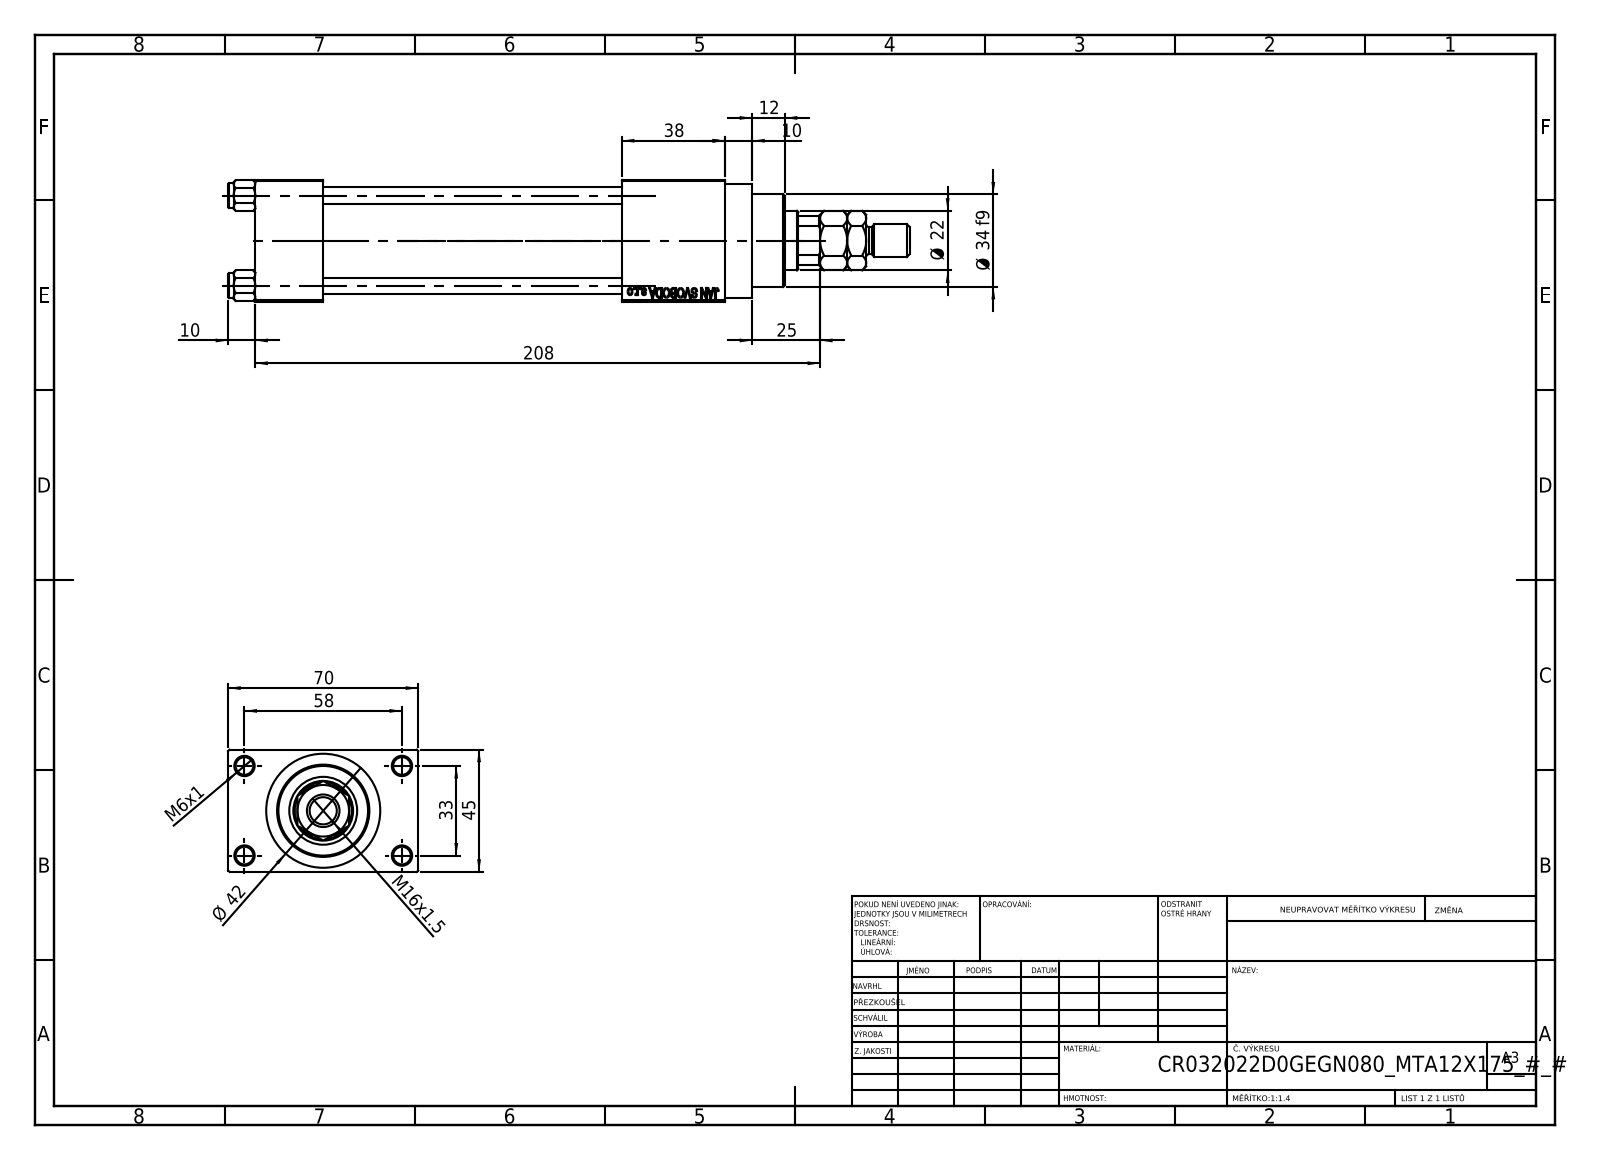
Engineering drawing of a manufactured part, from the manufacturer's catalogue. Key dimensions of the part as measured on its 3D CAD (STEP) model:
Part name (STEP PRODUCT): V215CR_VCP_D; V215_VC_A; V215CR_D_TYCINKA; NUT_M5_D (+2 more)
STEP written by: SolidWorks 2019 (CONFIG_CONTROL_DESIGN)
Units: millimetres
Bodies: 12 solids, 1152 faces (511 planar, 93 cylindrical, 548 other)
Overall size (bounding box): 251 × 70 × 45
Volume: 300 987 mm³ · Surface area: 103 637 mm²
Round holes (diameter × count): ⌀6 ×4, ⌀6.5 ×4, ⌀7 ×2, ⌀13.16 ×2, ⌀20 ×2, ⌀10.5 ×1, ⌀22 ×1, ⌀24 ×1, ⌀25 ×1, ⌀32 ×1, ⌀33 ×1
Round bosses / shafts (diameter × count): ⌀9 ×4, ⌀42 ×1, ⌀38 ×1, ⌀34 ×1, ⌀12 ×1, ⌀10 ×1
Partial cylindrical surfaces — rounded edges, fillets, slot ends (radius × count): R10.5 ×1
Main face-to-face distances: 45, 25, 12.5, 57.5, 110, 135, 148, 70, 38, 173
Hole centre spacings: 12.4, 23.48, 33.2, 33.37, 35.35, 45.6, 56.35, 33
